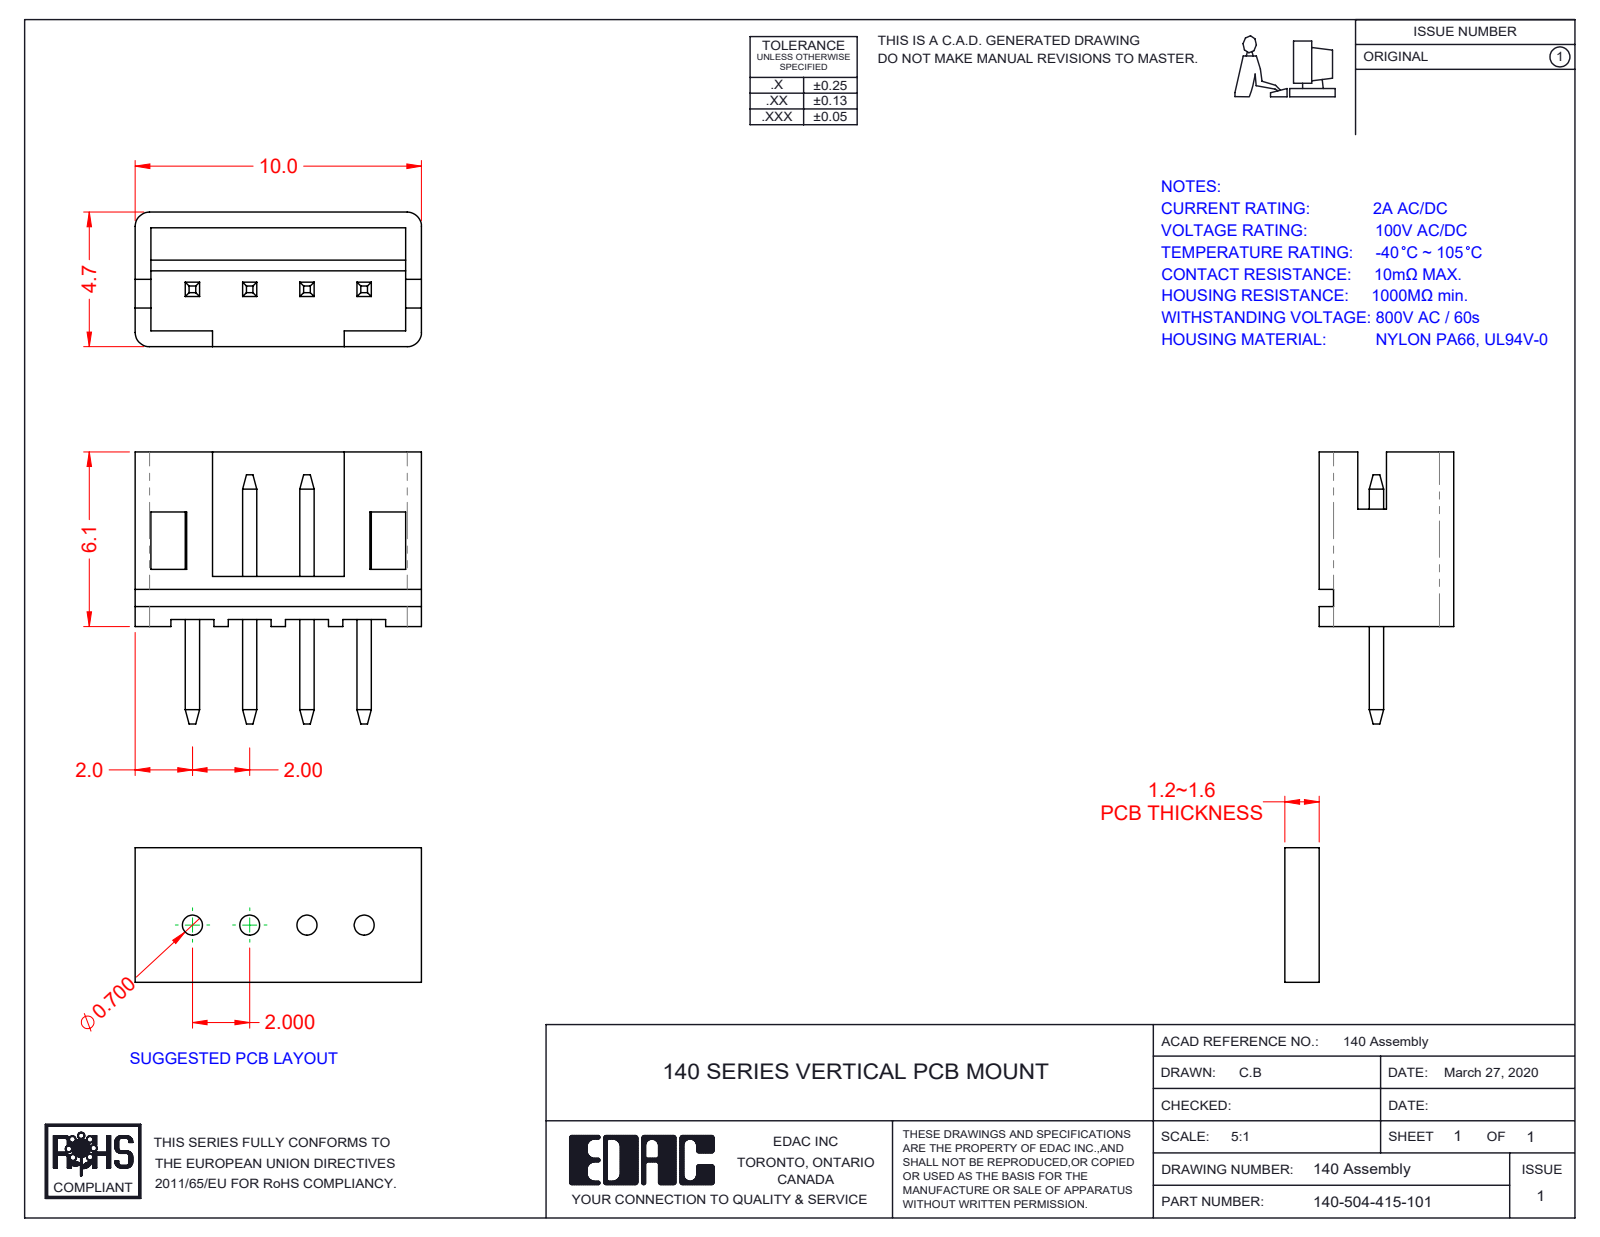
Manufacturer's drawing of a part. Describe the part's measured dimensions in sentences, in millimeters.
The part is named "V LI Housing_504; 140-504-415-101; V LI Contact_Str". Its 3-D file was written by "SolidWorks 2020 (CONFIG_CONTROL_DESIGN)". It is 5 solids with 128 faces: 122 planar, 6 cylindrical and 0 other. Overall it measures 10 by 9.5 by 4.7 millimeters. Its volume is 119 cubic millimeters and its surface area 440 square millimeters. Partial cylindrical surfaces (rounded edges, fillets, slot ends): 4 of radius 0.5. The main face-to-face distances are 0.55, 1.75, 0.5, 1.5, 4.15, 2, 9.45, 2.25, 4.7, 1.2.
